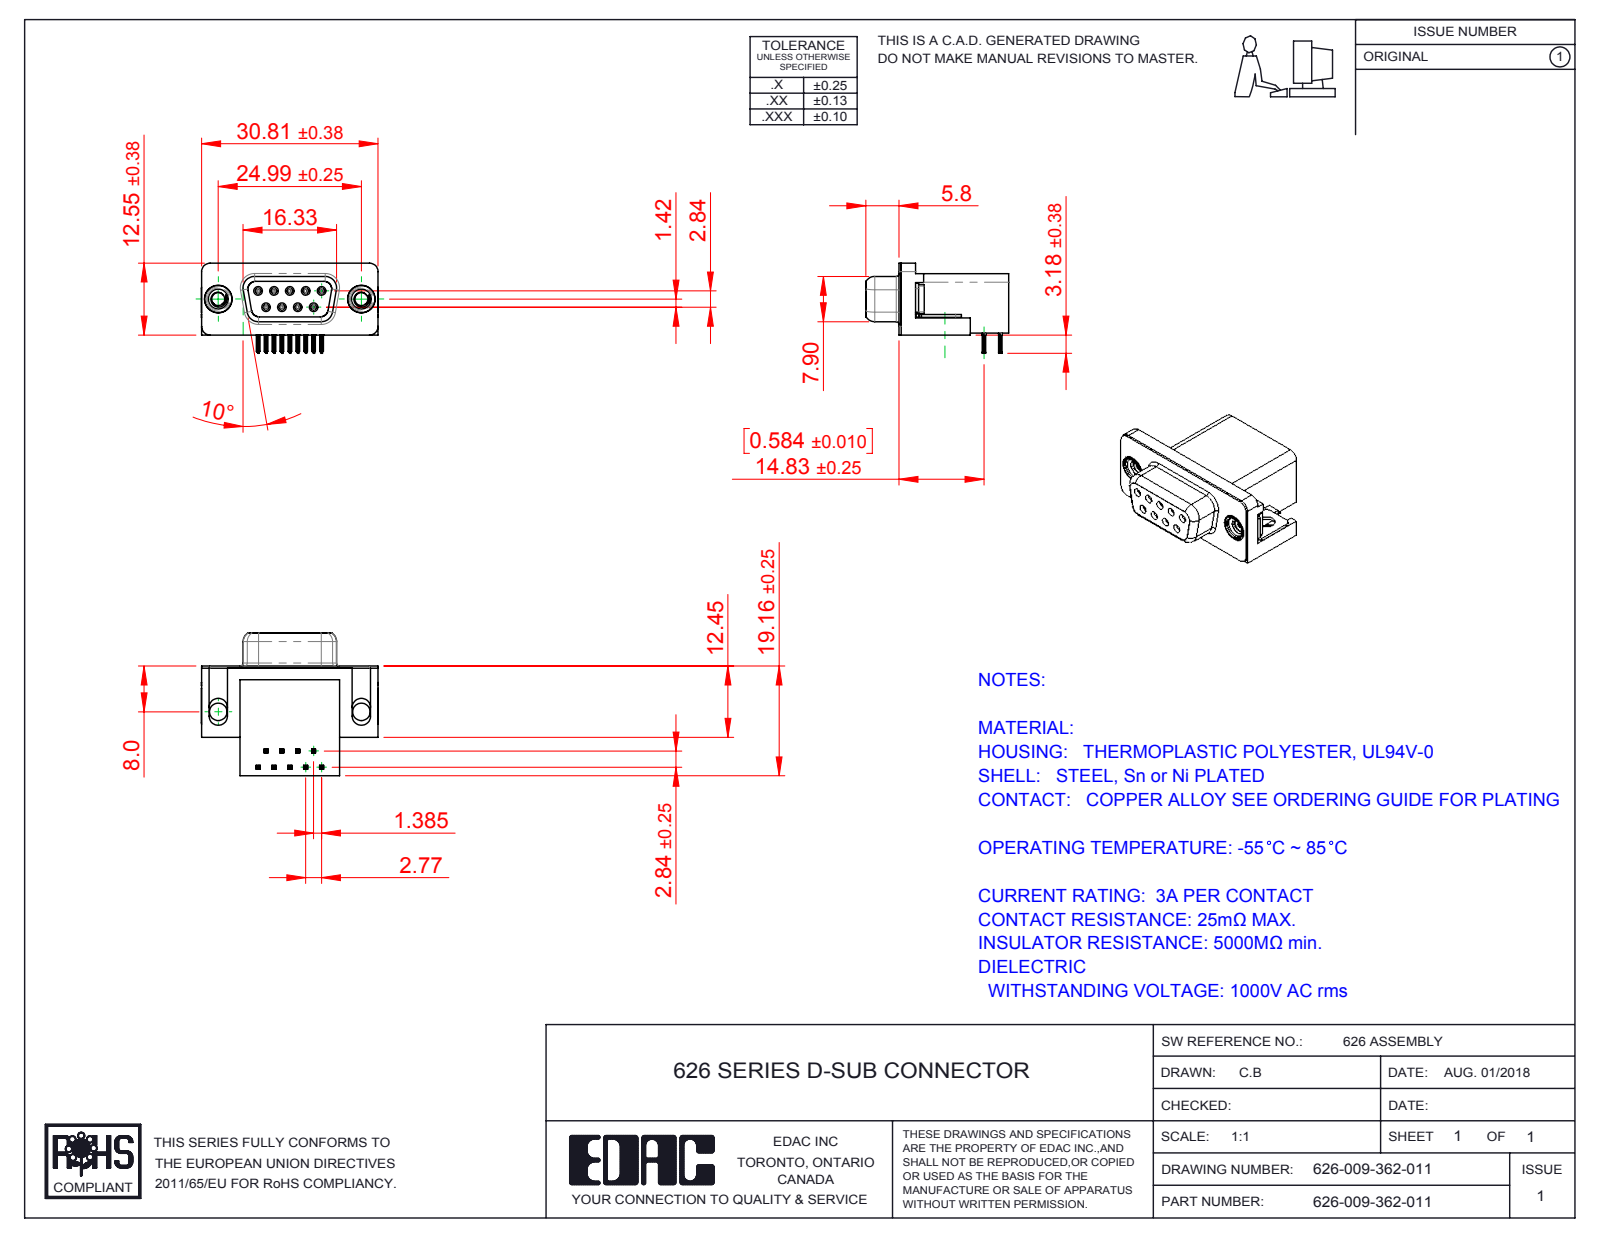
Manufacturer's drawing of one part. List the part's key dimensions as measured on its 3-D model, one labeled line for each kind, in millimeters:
Part name (STEP PRODUCT): 626-009-362-011; 626 4-40 Threaded Rivet; 626 Contact Top; 626 Shell_9 Socket (+3 more)
STEP written by: SolidWorks 2016 (CONFIG_CONTROL_DESIGN)
Units: millimetres
Bodies: 15 solids, 1572 faces (684 planar, 416 cylindrical, 472 other)
Overall size (bounding box): 30.89 × 24.96 × 15.73
Volume: 4 967 mm³ · Surface area: 5 778 mm²
Round holes (diameter × count): ⌀0.8 ×9, ⌀0.9 ×9, ⌀2.26 ×2, ⌀3.05 ×2, ⌀4 ×2, ⌀4.8 ×2, ⌀5 ×2
Round bosses / shafts (diameter × count): ⌀1.2 ×9, ⌀4.9 ×2, ⌀4.75 ×2, ⌀3.9 ×2
Partial cylindrical surfaces — rounded edges, fillets, slot ends (radius × count): R0.1 ×72, R0.15 ×36, R0.35 ×18, R1 ×18, R0.34 ×9, R0.25 ×8, R1.35 ×8, R1.6 ×8
Main face-to-face distances: 0.4, 10.34, 0.35, 18.76, 19.16, 2.9, 2.5, 6.2, 16.26, 0.5
Hole centre spacings: 3.16, 2.77, 5.54, 5.03, 5.04, 8.31, 7.48, 7.49
